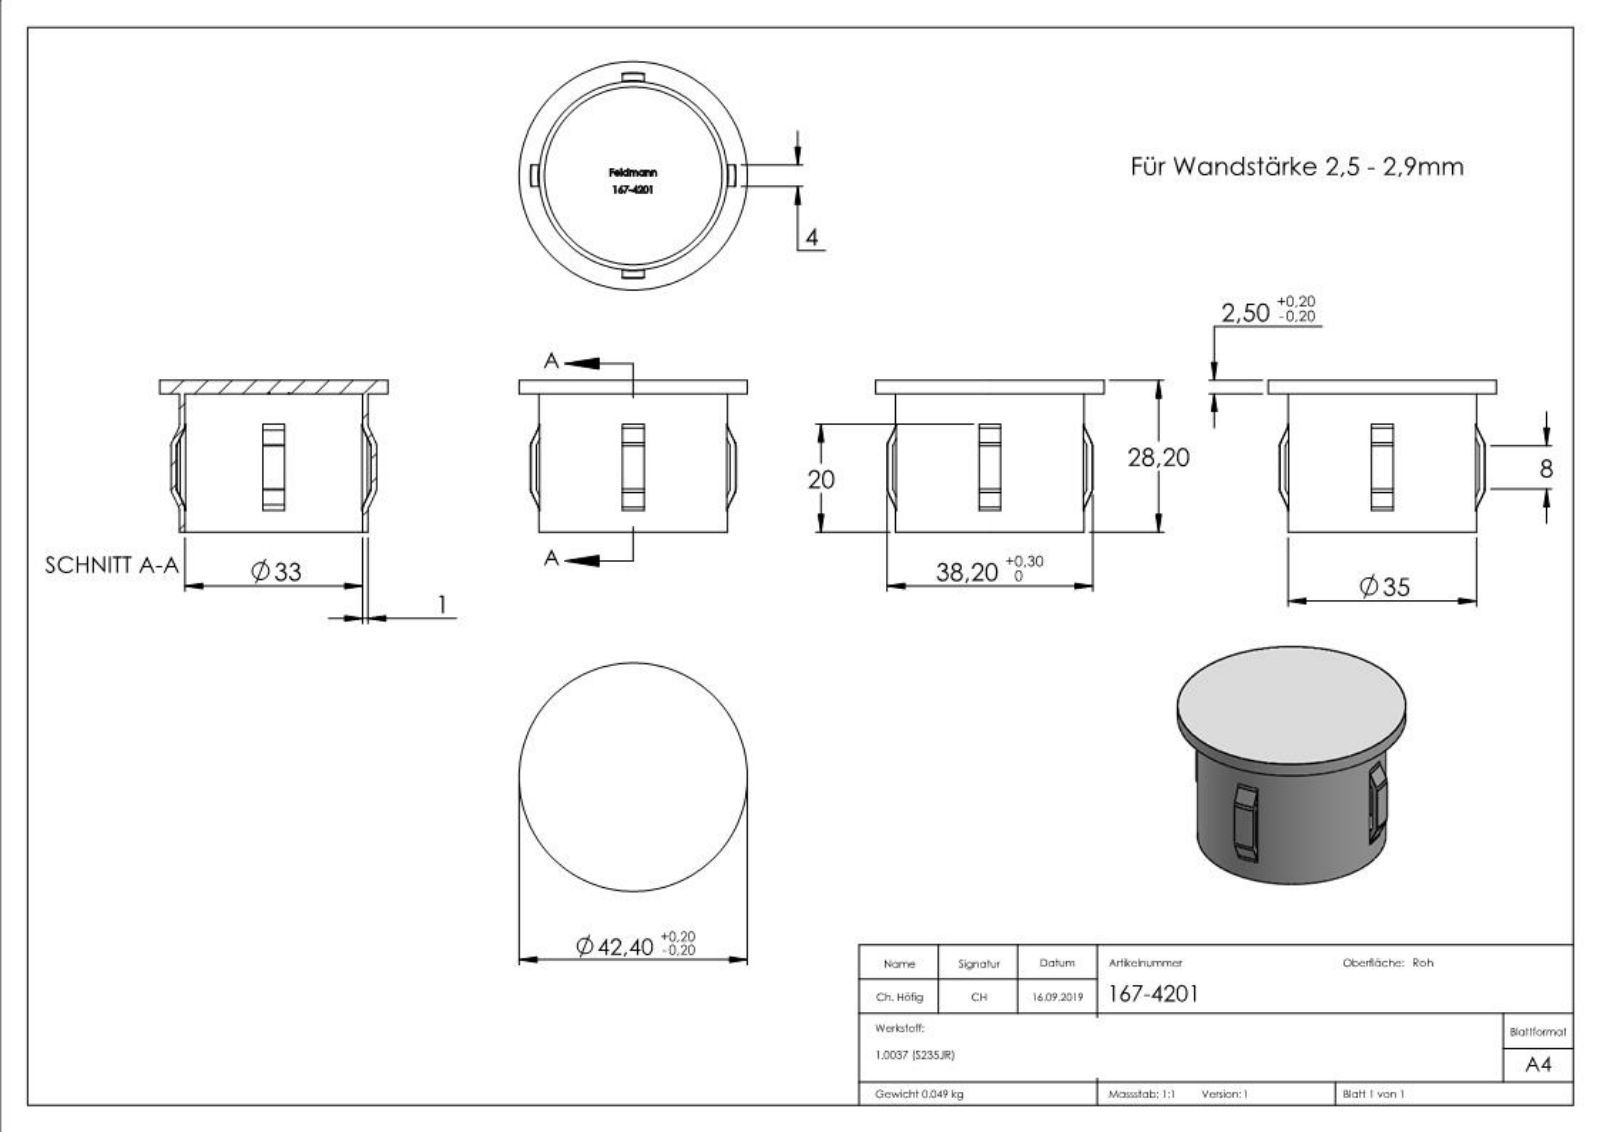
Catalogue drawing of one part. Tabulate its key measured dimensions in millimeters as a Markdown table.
| quantity | value |
| --- | --- |
| part name | 167-4201 |
| STEP written by | SolidWorks 2015 (CONFIG_CONTROL_DESIGN) |
| units | millimeters |
| bodies | 1 solid, 288 faces (140 planar, 16 cylindrical, 132 other) |
| overall size | 42.4 × 42.4 × 28.2 |
| volume | 6 285 mm³ |
| surface area | 8 890 mm² |
| round holes (diameter × count) | 33 × 1 |
| round bosses / shafts (diameter × count) | 42.4 × 1, 35 × 1 |
| partial cylindrical surfaces (radius × count) | 18.1 × 1, 19.1 × 1 |
| main face-to-face distances | 2.5, 25.7, 28.2, 4, 2.4, 25.8, 3.88, 2.85, 2, 1.26 |
